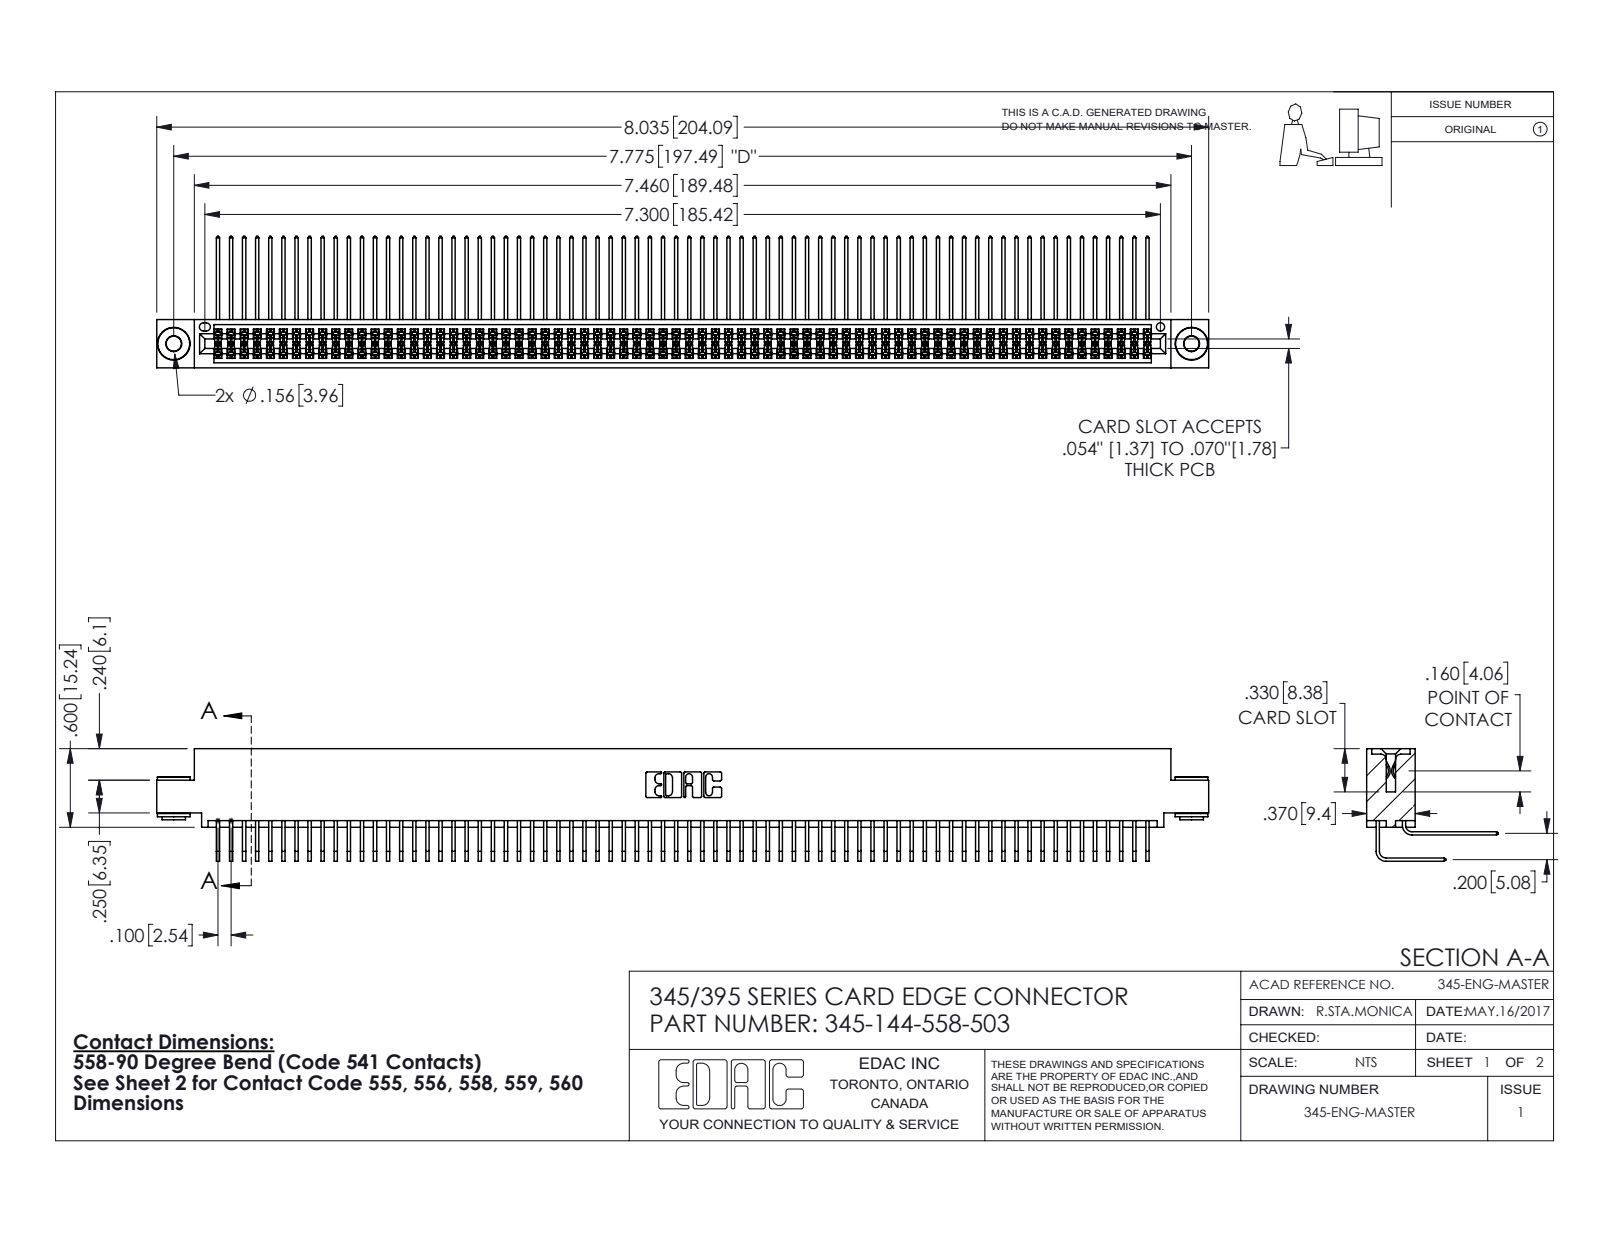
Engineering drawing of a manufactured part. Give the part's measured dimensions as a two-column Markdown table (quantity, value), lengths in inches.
| quantity | value |
| --- | --- |
| part name | 345-292-001_558 Tail - 2; 345 Part_0.110 Offset - 0.156 Dia-TH; 345-292-001_558 559 Tail - 1; 345-144-558-503 (+1 more) |
| STEP written by | SolidWorks 2016 (CONFIG_CONTROL_DESIGN) |
| units | inches |
| bodies | 147 solids, 7656 faces (5134 planar, 2514 cylindrical, 8 other) |
| overall size | 8.035 × 1.005 × 0.859 |
| volume | 1.274 in³ |
| surface area | 55.26 in² |
| round holes (diameter × count) | 0.116 × 2, 0.156 × 2, 0.064 × 1 |
| round bosses / shafts (diameter × count) | 0.25 × 2, 0.18 × 2, 0.136 × 2 |
| partial cylindrical surfaces (radius × count) | 0.006 × 288, 0.01 × 22, 0.007 × 6, 0.031 × 6, 0.026 × 3, 0.014 × 2, 0.019 × 2, 0.022 × 2 |
| main face-to-face distances | 0.072, 0.298, 0.2, 0.025, 0.37, 0.098, 0.272, 0.225, 0.025, 0.175 |
| hole center spacings | 0.27, 7.539, 7.775 |
